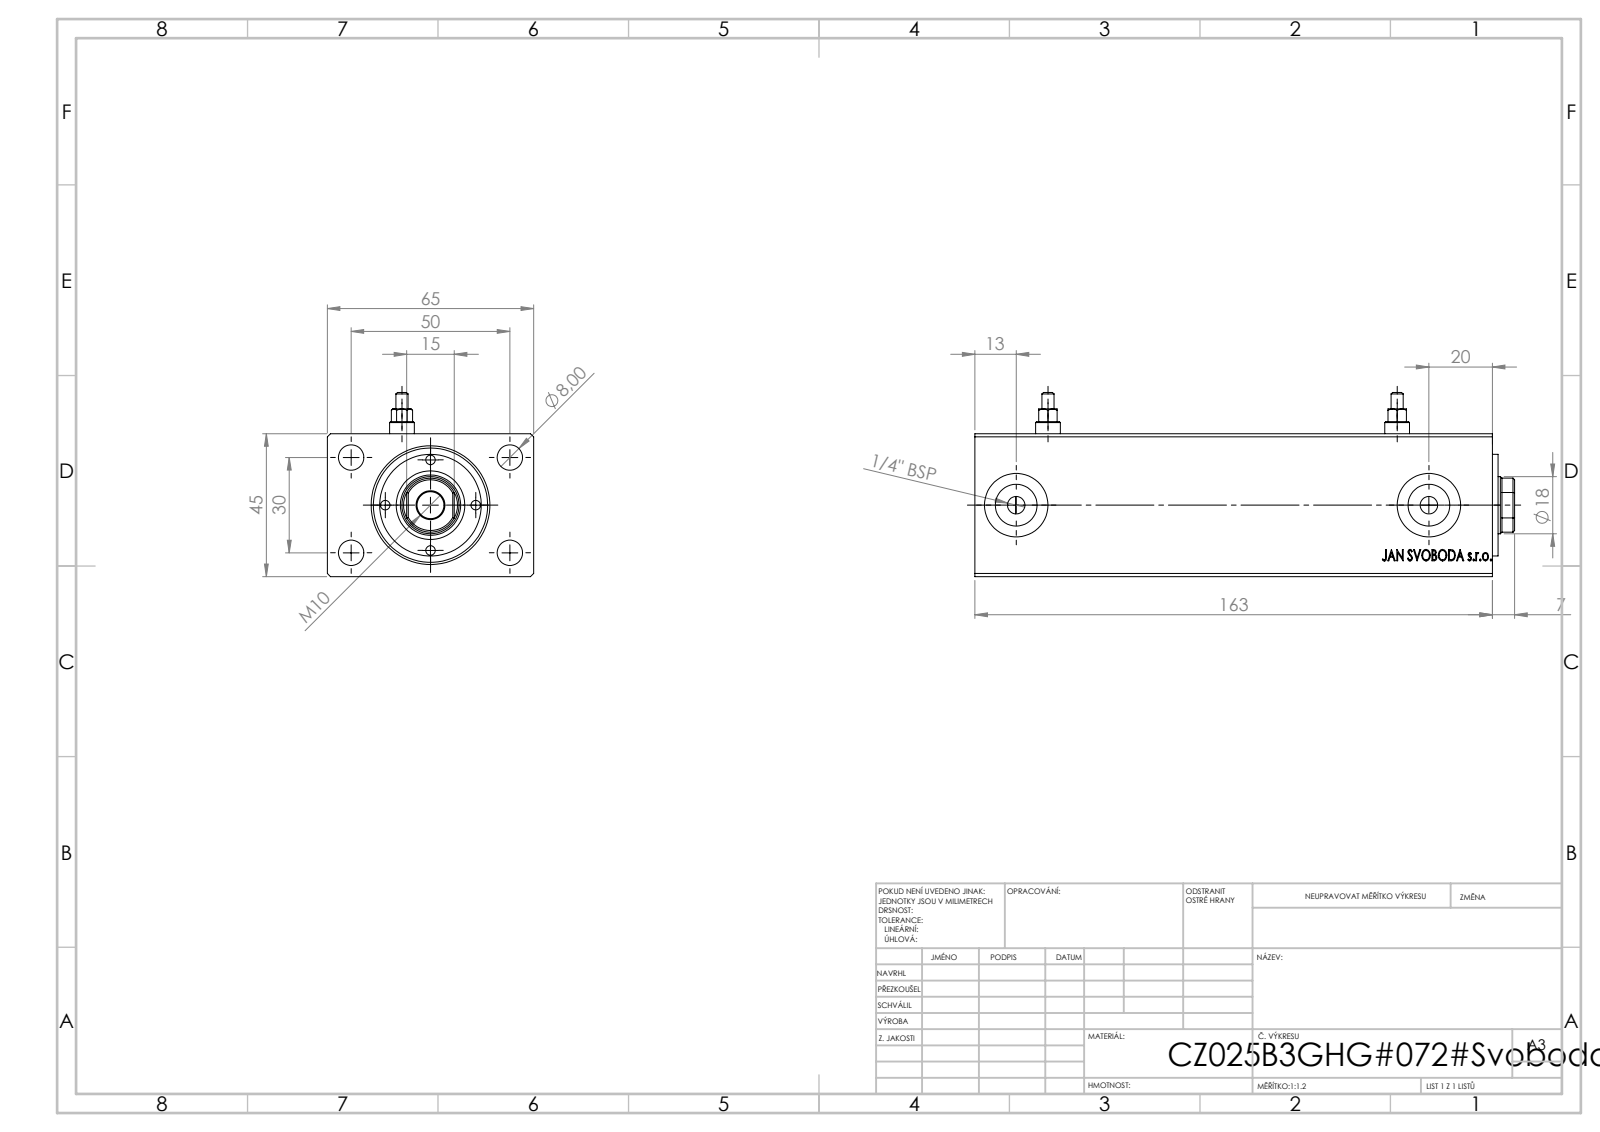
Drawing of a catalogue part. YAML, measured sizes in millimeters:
part_name: "Zatka_Cushioning3; V500CZ_B_VC; V500CZ"
step_written_by: "SolidWorks 2019 (CONFIG_CONTROL_DESIGN)"
units: millimeters
bodies: {solids: 5, faces: 933, planar: 423, cylindrical: 74, other: 436}
overall_size: [170, 65, 58]
volume: 445830
surface_area: 75016
round_holes:
  - {diameter: 8, count: 6}
  - {diameter: 3, count: 4}
  - {diameter: 1.8, count: 2}
  - {diameter: 5.5, count: 2}
  - {diameter: 13.16, count: 2}
  - {diameter: 20, count: 2}
  - {diameter: 8.5, count: 1}
  - {diameter: 18, count: 1}
  - {diameter: 19, count: 1}
  - {diameter: 25, count: 1}
  - {diameter: 36, count: 1}
round_bosses_or_shafts:
  - {diameter: 7.8, count: 2}
  - {diameter: 3.8, count: 2}
  - {diameter: 32, count: 1}
partial_cylinders:
  - {radius: 8.5, count: 1}
face_to_face_distances: [45, 65, 163, 7, 162.8, 12.8, 150.2, 12.6, 1.8, 5.2]
hole_center_spacings: [14.25, 18.45, 20.15, 25.01, 29.15, 38.48, 42.02, 28.5]
